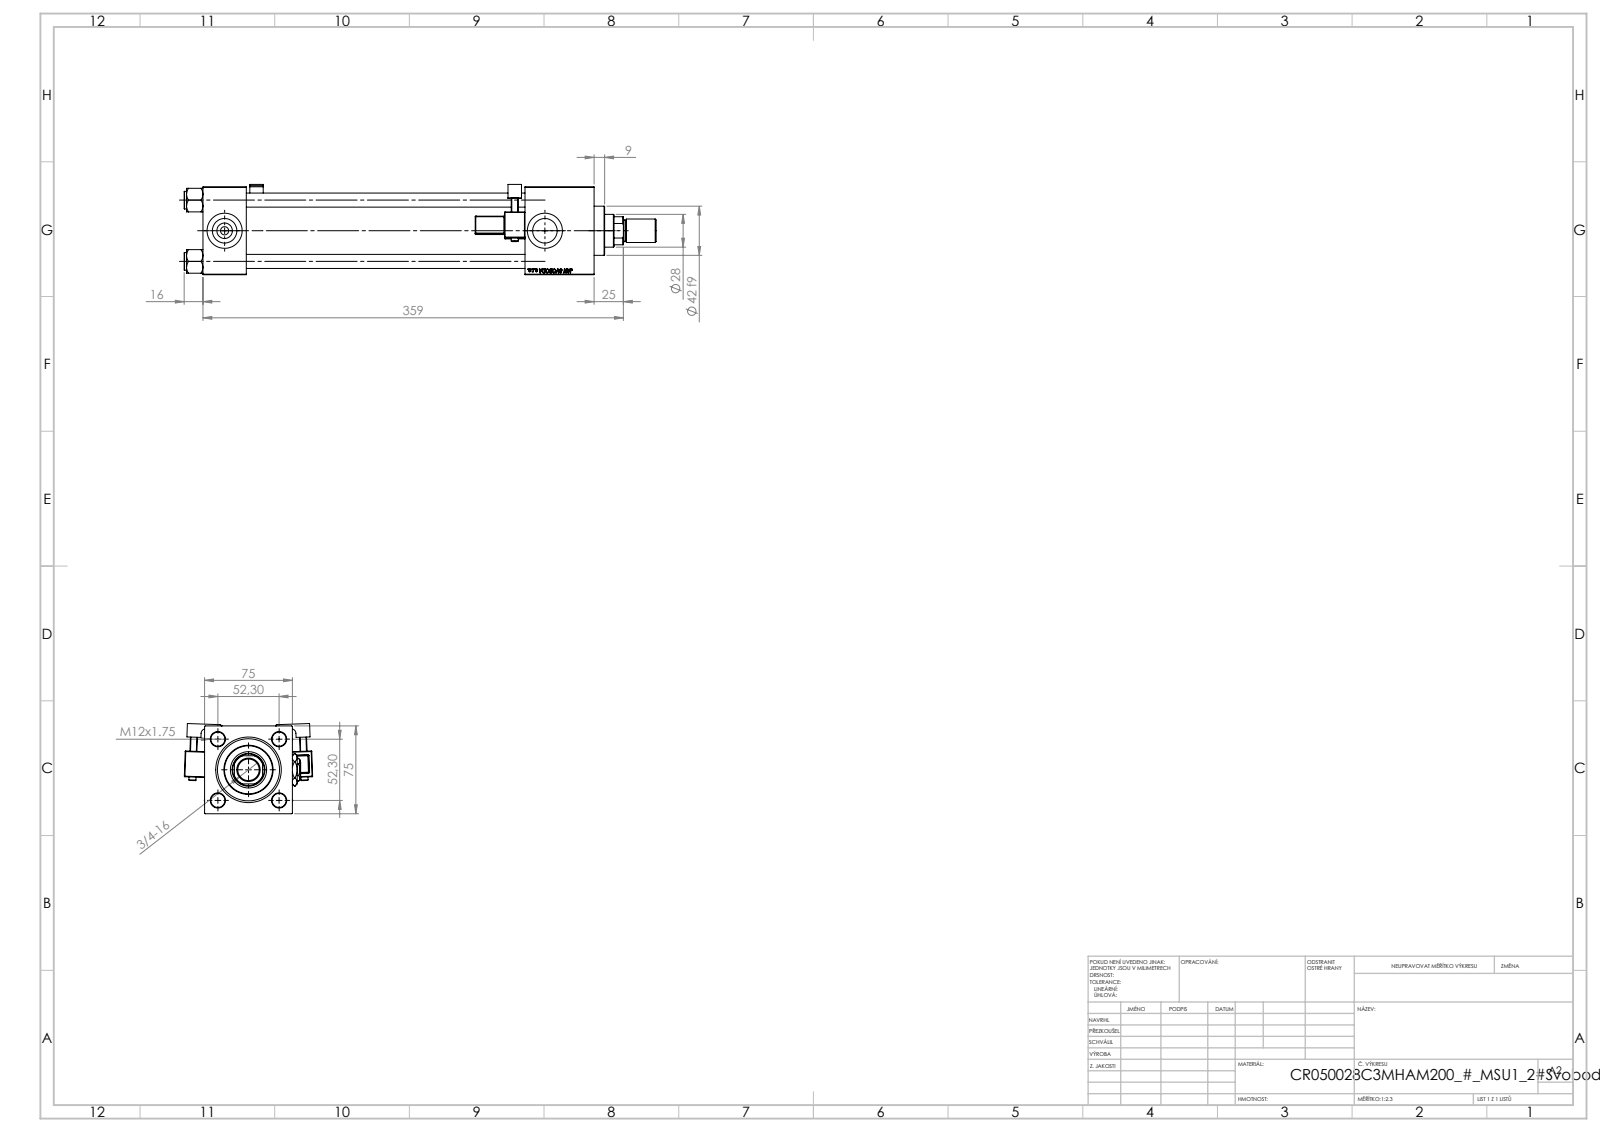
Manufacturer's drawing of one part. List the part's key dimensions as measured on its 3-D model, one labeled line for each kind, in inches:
Part name (STEP PRODUCT): NUT_M5_C; V215CR_MSU; V215CR_C_TYCINKA; Zatka_pro_OIL_PORT (+4 more)
STEP written by: SolidWorks 2019 (CONFIG_CONTROL_DESIGN)
Units: inches
Bodies: 16 solids, 1417 faces (635 planar, 162 cylindrical, 620 other)
Overall size (bounding box): 15.866 × 4.314 × 3.033
Volume: 60.78 in³ · Surface area: 423.2 in²
Round holes (diameter × count): ⌀0.472 ×4, ⌀0.276 ×2, ⌀0.825 ×2, ⌀1.181 ×2, ⌀0.728 ×1, ⌀1.102 ×1, ⌀1.22 ×1, ⌀1.614 ×1, ⌀1.969 ×1, ⌀2.087 ×1
Round bosses / shafts (diameter × count): ⌀0.591 ×4, ⌀0.236 ×2, ⌀2.205 ×1, ⌀1.654 ×1, ⌀0.787 ×1, ⌀0.709 ×1
Partial cylindrical surfaces — rounded edges, fillets, slot ends (radius × count): R0.02 ×48, R0.039 ×2, R0.098 ×2, R0.157 ×2, R0.531 ×1
Main face-to-face distances: 2.953, 1.457, 10.827, 9.37, 13.15, 11.693, 2.323, 12.02, 10.563, 1.193
Hole centre spacings: 1.456, 2.059, 2.912, 10.768
